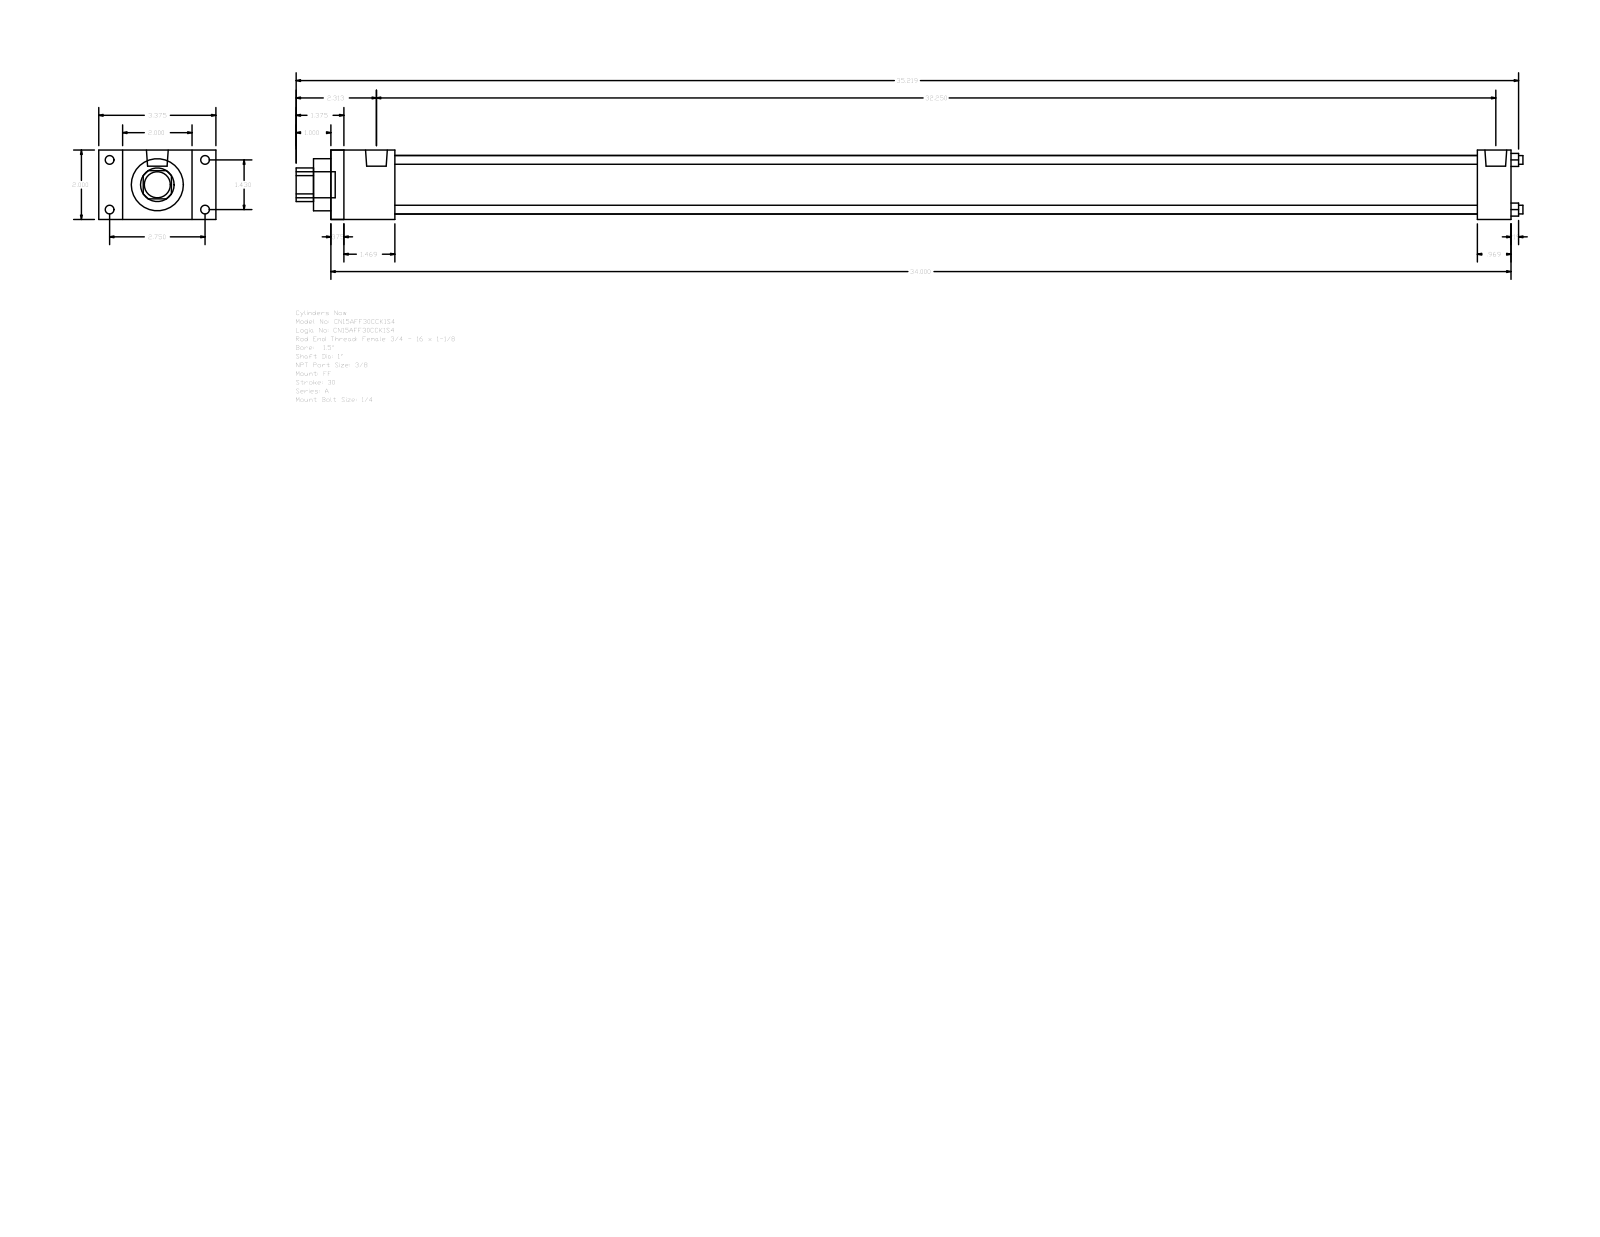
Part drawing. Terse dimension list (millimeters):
name: A_FF__0150_1
written by: GSSL Pune (CONFIG_CONTROL_DESIGN)
unit: mm
bodies: 0 solids, 92 faces (64 planar, 28 cylindrical, 0 other)
size: 897.73 × 85.72 × 50.8
holes: 4× ⌀6.35, 1× ⌀25.4, 1× ⌀38.1, 1× ⌀42.93
bosses: 4× ⌀6.35, 4× ⌀5.56, 2× ⌀15.93, 1× ⌀19.05
rounds: 1× R12.29
face distances: 50.8, 863.6, 9.52, 854.08, 46.83, 838.99, 37.31, 829.47, 792.16, 816.77
hole spacings: 25.68, 36.32, 51.36
